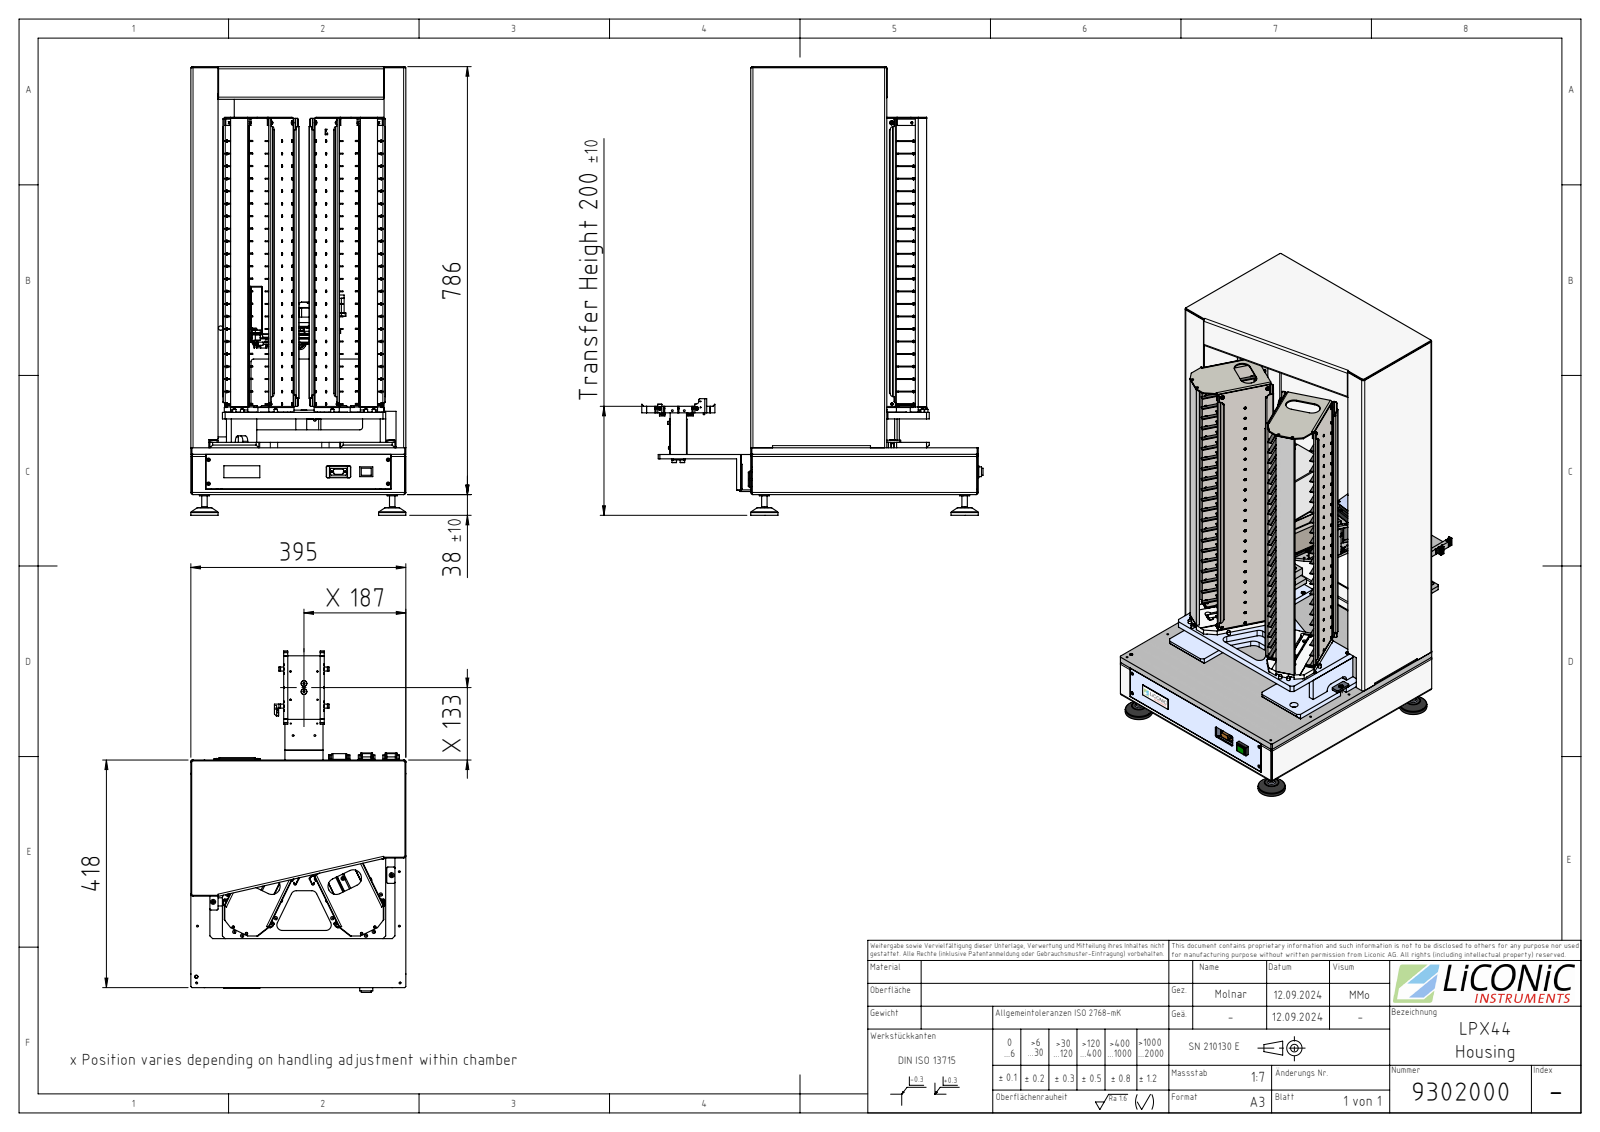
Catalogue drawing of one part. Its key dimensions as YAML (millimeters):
part_name: "9302000"
step_written_by: "SolidWorks 2022 (AUTOMOTIVE_DESIGN)"
units: millimeters
bodies: {solids: 43, faces: 3938, planar: 2142, cylindrical: 1695, other: 101}
overall_size: [824, 626.49, 395.01]
volume: 6805000
surface_area: 3796000
round_holes:
  - {diameter: 4, count: 96}
  - {diameter: 3.3, count: 45}
  - {diameter: 2.5, count: 31}
  - {diameter: 4.2, count: 31}
  - {diameter: 8, count: 19}
  - {diameter: 4.5, count: 14}
  - {diameter: 5.3, count: 10}
  - {diameter: 3.1, count: 8}
  - {diameter: 4.7, count: 8}
  - {diameter: 6, count: 8}
  - {diameter: 12.5, count: 8}
  - {diameter: 5, count: 7}
round_bosses_or_shafts:
  - {diameter: 50.01, count: 4}
  - {diameter: 10, count: 4}
  - {diameter: 1.5, count: 3}
  - {diameter: 15.5, count: 1}
  - {diameter: 14.5, count: 1}
partial_cylinders:
  - {radius: 2, count: 484}
  - {radius: 2.5, count: 112}
  - {radius: 1, count: 78}
  - {radius: 4, count: 35}
  - {radius: 1.5, count: 24}
  - {radius: 5, count: 18}
  - {radius: 6, count: 16}
  - {radius: 3, count: 12}
face_to_face_distances: [2, 393, 1, 12, 72, 90, 86, 784, 74, 395]
hole_center_spacings: [23, 46, 69, 92, 115, 138, 161, 184]
